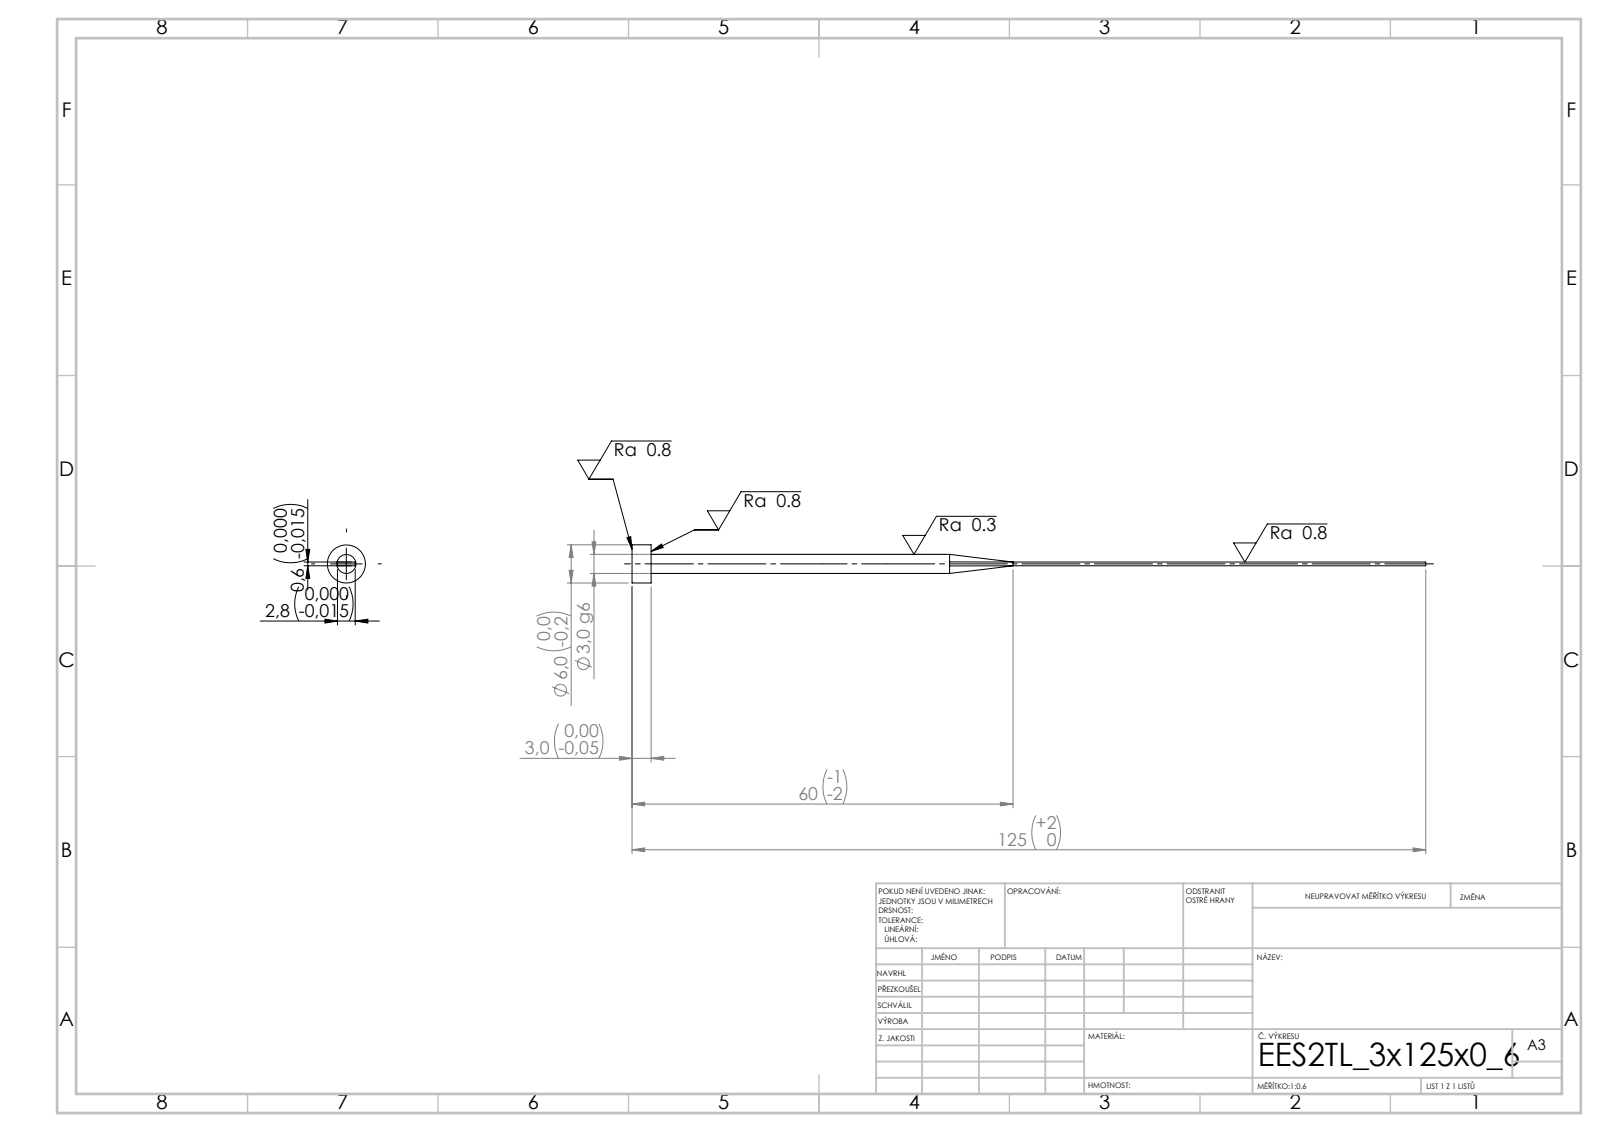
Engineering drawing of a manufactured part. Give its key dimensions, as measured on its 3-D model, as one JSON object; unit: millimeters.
{"step_written_by": "SolidWorks 2019 (CONFIG_CONTROL_DESIGN)", "units": "millimeters", "bodies": {"solids": 1, "faces": 15, "planar": 7, "cylindrical": 4, "other": 4}, "overall_size": [125, 6, 6], "volume_mm3": 568, "surface_area_mm2": 1070, "round_bosses_or_shafts": [[6, 1], [3, 1]], "face_to_face_distances": [0.6, 2.8, 3, 125, 122]}
